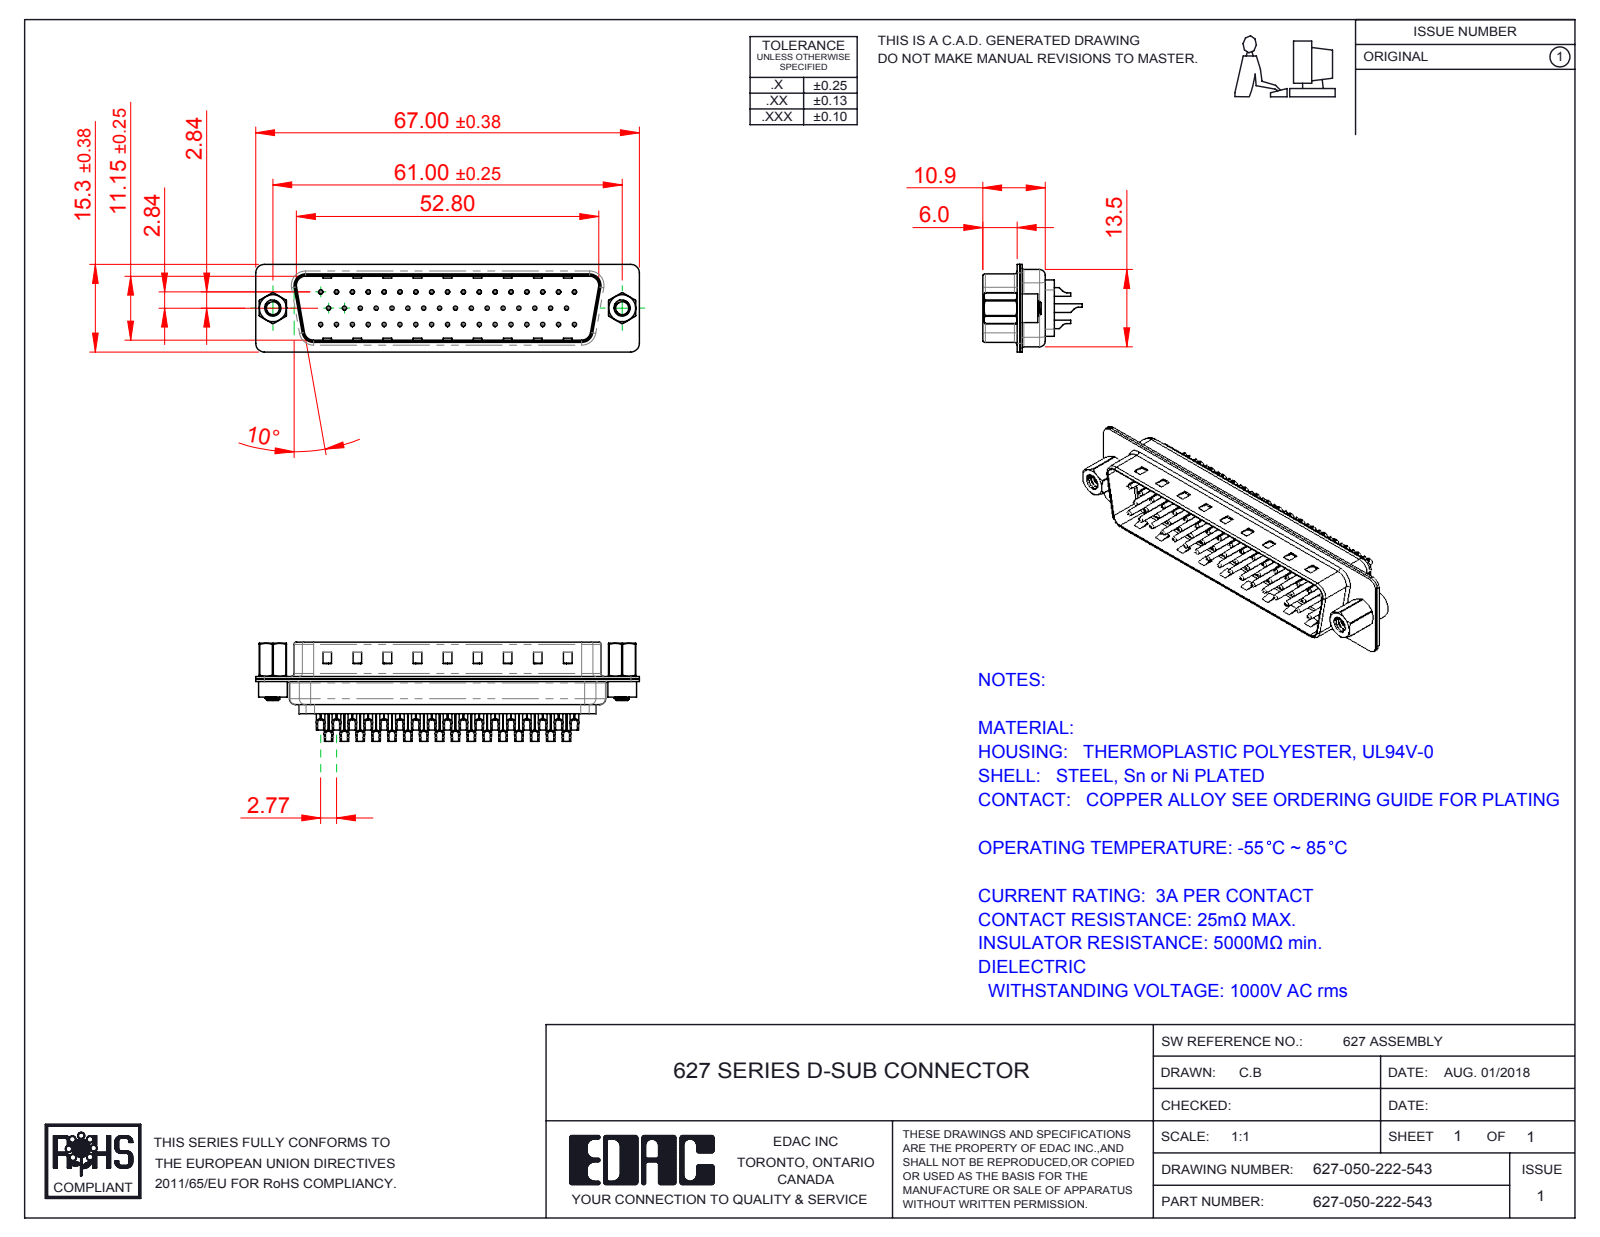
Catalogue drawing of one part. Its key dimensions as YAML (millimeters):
part_name: "627-050-222-543; 627 4-40 Hex Standoff; 627 4-40 Threaded Rivet; 627 Contact Row 3_22L (+5 more)"
step_written_by: "SolidWorks 2016 (CONFIG_CONTROL_DESIGN)"
units: millimeters
bodies: {solids: 57, faces: 3738, planar: 925, cylindrical: 1663, other: 1150}
overall_size: [67, 17.35, 15.3]
volume: 4682
surface_area: 13447
round_holes:
  - {diameter: 0.35, count: 50}
  - {diameter: 1.1, count: 50}
  - {diameter: 1.6, count: 50}
  - {diameter: 2.26, count: 2}
  - {diameter: 2.29, count: 2}
  - {diameter: 4, count: 2}
  - {diameter: 4.8, count: 2}
round_bosses_or_shafts:
  - {diameter: 2, count: 50}
  - {diameter: 1.5, count: 50}
  - {diameter: 0.75, count: 50}
  - {diameter: 5, count: 2}
  - {diameter: 4.9, count: 2}
  - {diameter: 2.79, count: 2}
partial_cylinders:
  - {radius: 1.5, count: 16}
  - {radius: 2, count: 12}
  - {radius: 0.5, count: 8}
  - {radius: 1.6, count: 8}
  - {radius: 1, count: 7}
  - {radius: 0.25, count: 4}
  - {radius: 0.6, count: 4}
  - {radius: 0.65, count: 4}
face_to_face_distances: [0.4, 0.45, 11.55, 0.9, 6.05, 6.5, 0.78, 12.33, 1.95, 0.77]
hole_center_spacings: [3.16, 2.77, 5.54, 8.31, 11.08, 13.85, 16.62, 5.03]
